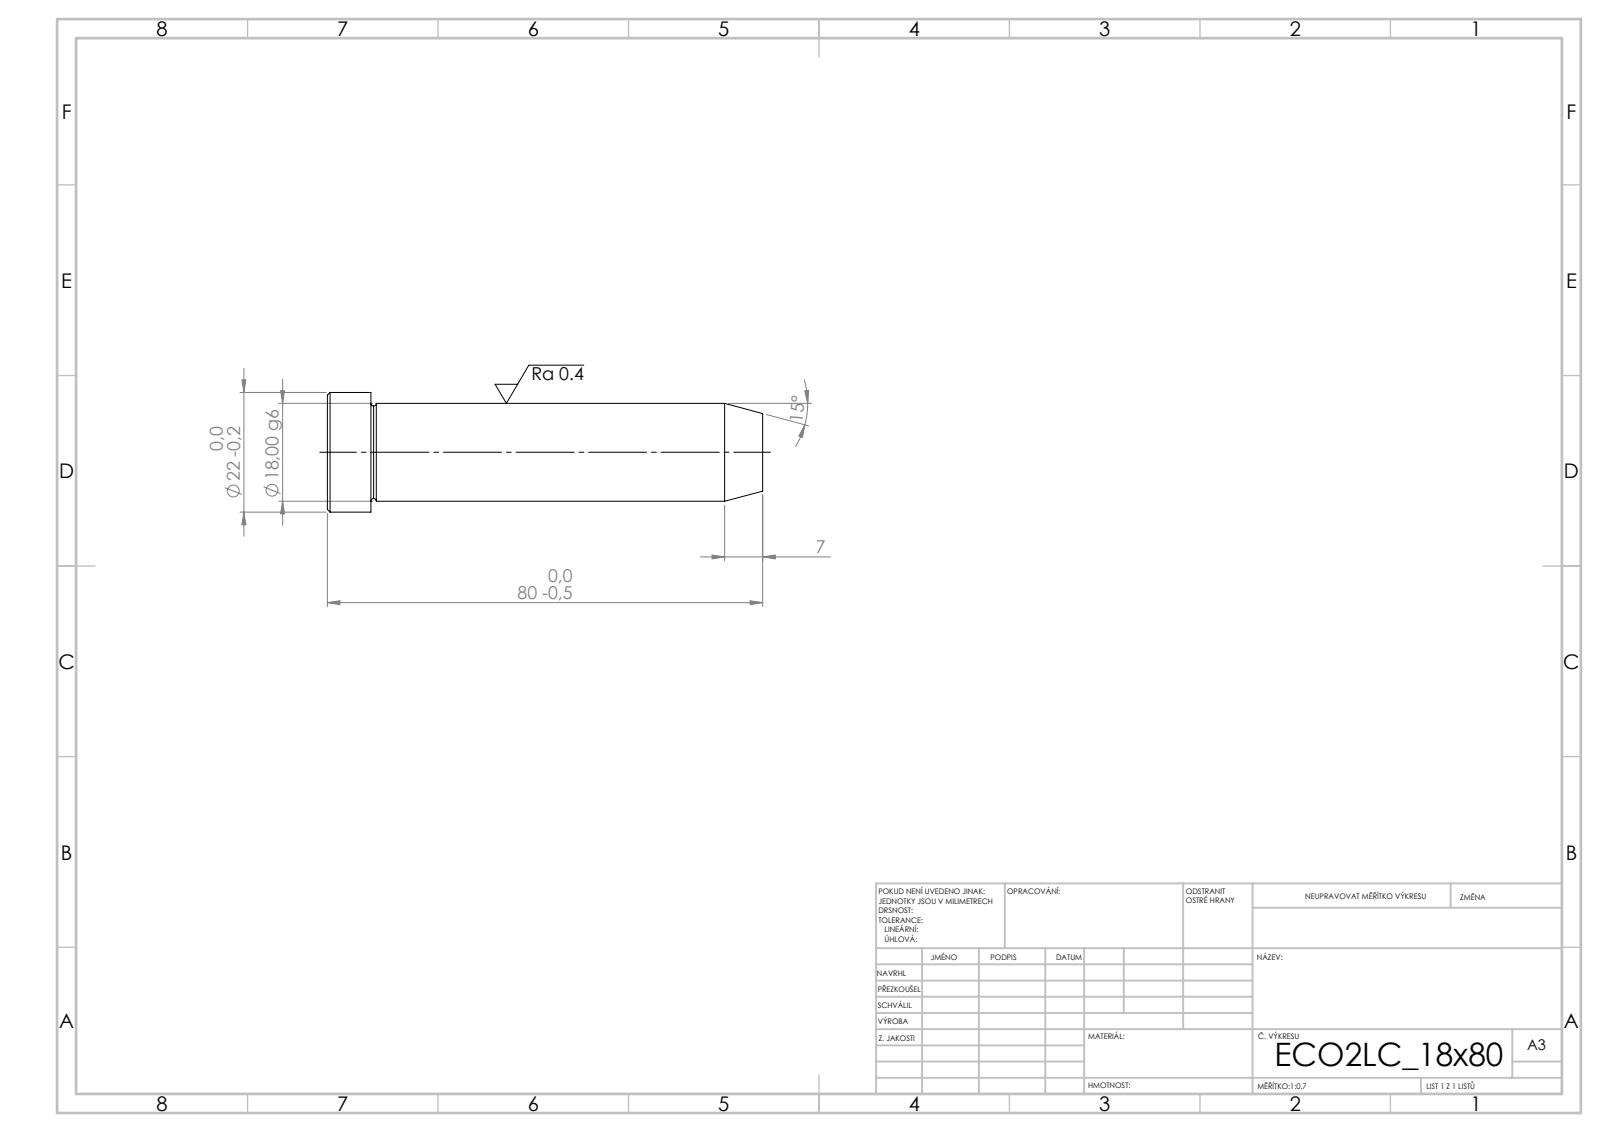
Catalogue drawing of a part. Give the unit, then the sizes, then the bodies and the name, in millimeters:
Units: millimetres
Overall size (bounding box): 80 × 22 × 22
Round bosses / shafts (diameter × count): ⌀22 ×1, ⌀18 ×1
Main face-to-face distances: 80, 72, 8
Volume: 20 987 mm³ · Surface area: 5 270 mm²
Bodies: 1 solid, 15 faces (3 planar, 4 cylindrical, 8 other)
STEP written by: SolidWorks 2019 (CONFIG_CONTROL_DESIGN)
